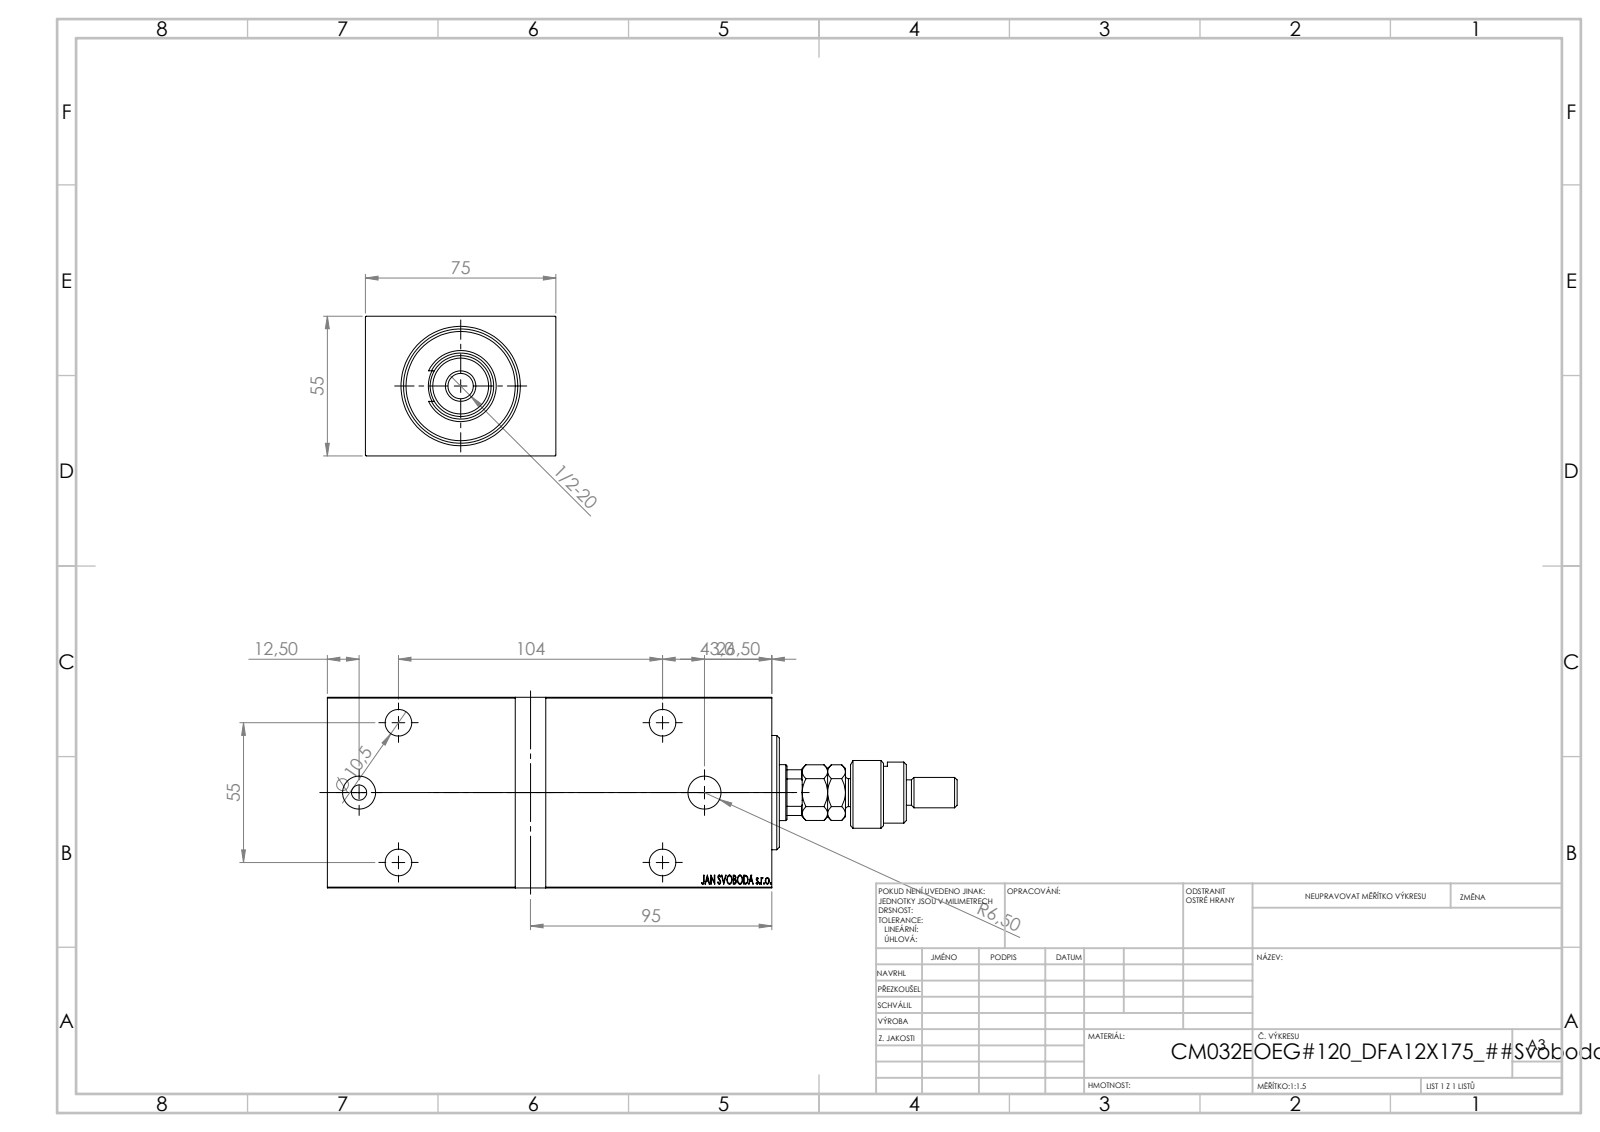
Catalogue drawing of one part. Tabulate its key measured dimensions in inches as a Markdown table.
| quantity | value |
| --- | --- |
| part name | V450CM_E_VCP; V450CM_E_Body; V450CM_VC_B; FEMALE_PART_FOR_DFA (+1 more) |
| STEP written by | SolidWorks 2019 (CONFIG_CONTROL_DESIGN) |
| units | inches |
| bodies | 5 solids, 931 faces (436 planar, 57 cylindrical, 438 other) |
| overall size | 9.764 × 2.953 × 2.165 |
| volume | 40.74 in³ |
| surface area | 166.4 in² |
| round holes (diameter × count) | 0.413 × 5, 0.65 × 4, 0.512 × 2, 0.866 × 1, 1.004 × 1, 1.26 × 1, 1.772 × 1 |
| round bosses / shafts (diameter × count) | 1.339 × 1, 1.102 × 1, 0.945 × 1, 0.709 × 1, 0.472 × 1, 0.433 × 1, 0.394 × 1, 0.236 × 1 |
| partial cylindrical surfaces (radius × count) | 0.384 × 1, 0.413 × 1 |
| main face-to-face distances | 2.165, 2.953, 6.89, 0.118, 0.394, 6.496, 0.315, 0.197, 6.693, 6.299 |
| hole center spacings | 1.243, 1.263, 2.165, 4.094, 4.632, 4.828, 4.866, 5.354 |
